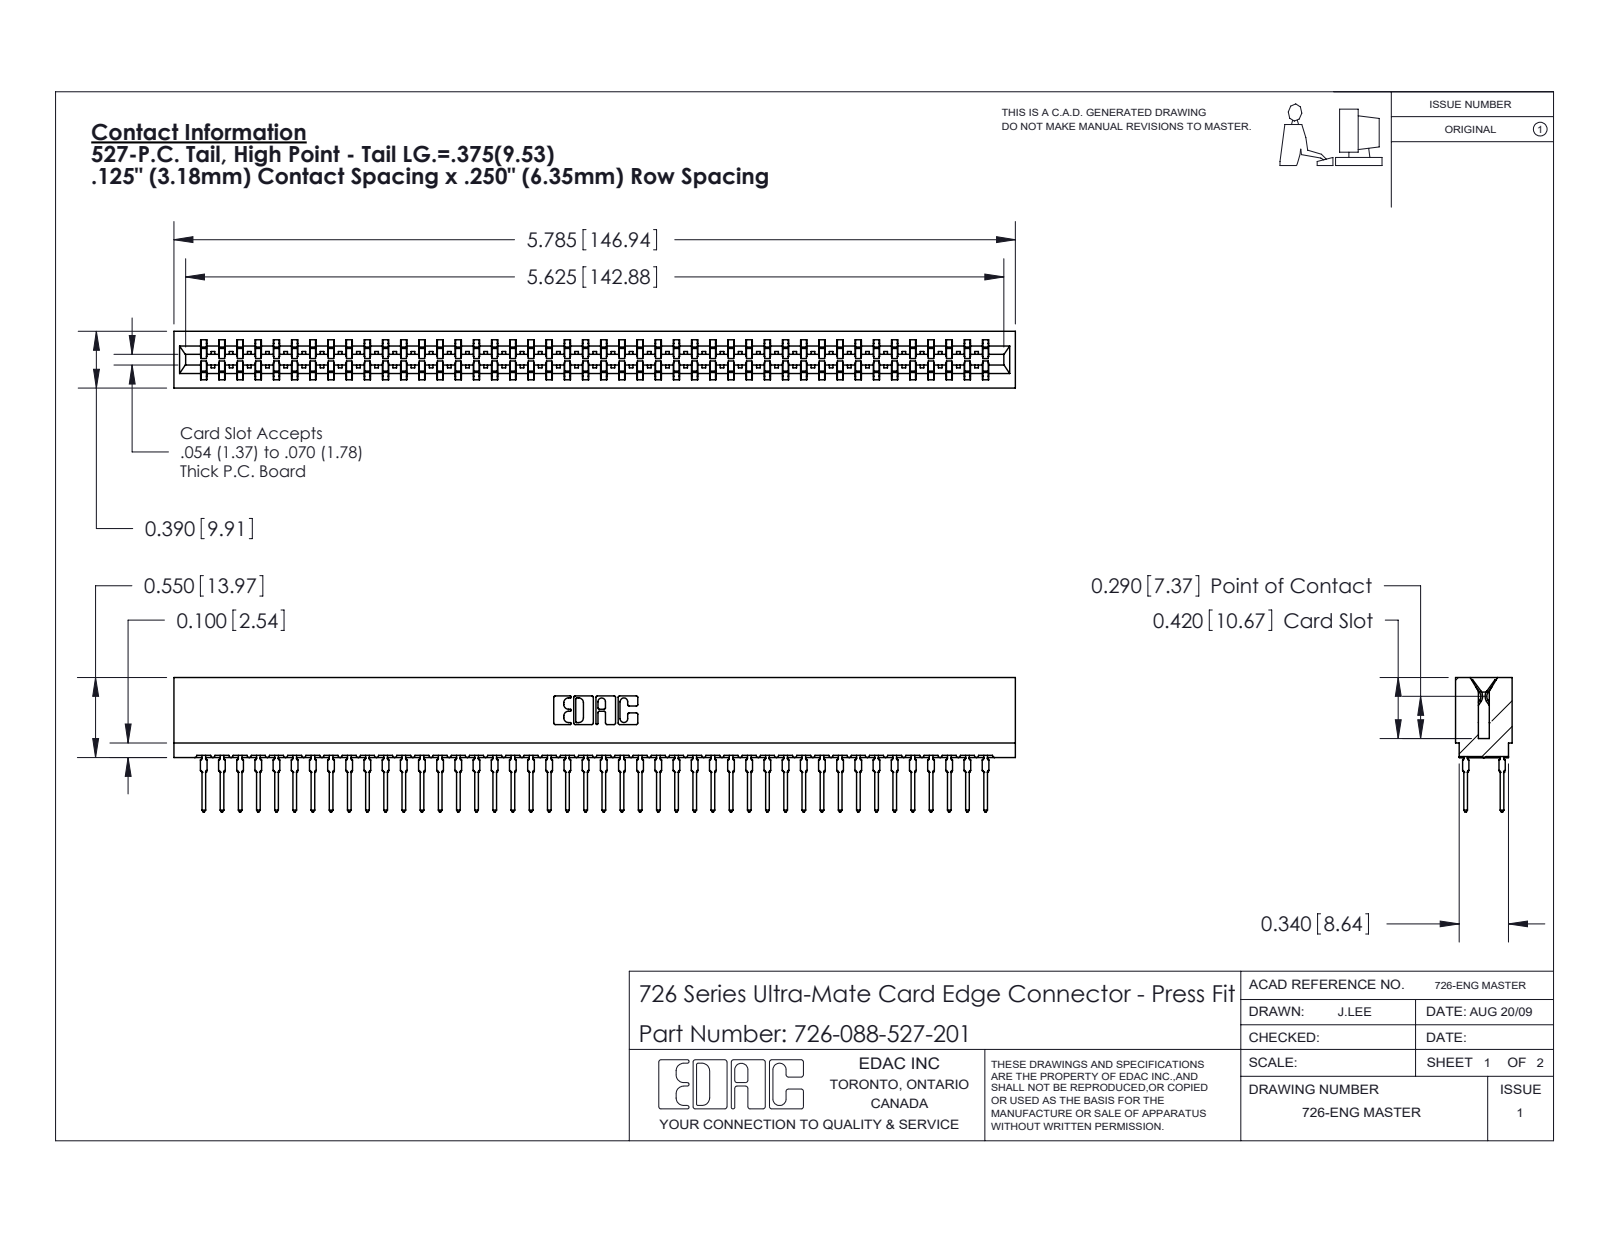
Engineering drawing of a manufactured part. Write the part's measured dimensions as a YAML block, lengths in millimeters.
part_name: "726 Part_.515 Slot Depth - 01; 726-088-527-201; 746-292-001_527"
step_written_by: "SolidWorks 2020 (CONFIG_CONTROL_DESIGN)"
units: millimeters
bodies: {solids: 89, faces: 7973, planar: 4103, cylindrical: 1582, other: 2288}
overall_size: [146.9, 23.5, 9.9]
volume: 13700
surface_area: 23490
partial_cylinders:
  - {radius: 0.5, count: 176}
  - {radius: 0.4, count: 45}
  - {radius: 0.3, count: 22}
  - {radius: 0.1, count: 8}
  - {radius: 0.3, count: 8}
  - {radius: 0.2, count: 6}
  - {radius: 0.8, count: 6}
  - {radius: 0.7, count: 3}
face_to_face_distances: [1.4, 8.5, 0.6, 7.8, 9.9, 6.4, 7, 2.1, 9.3, 0.8]
